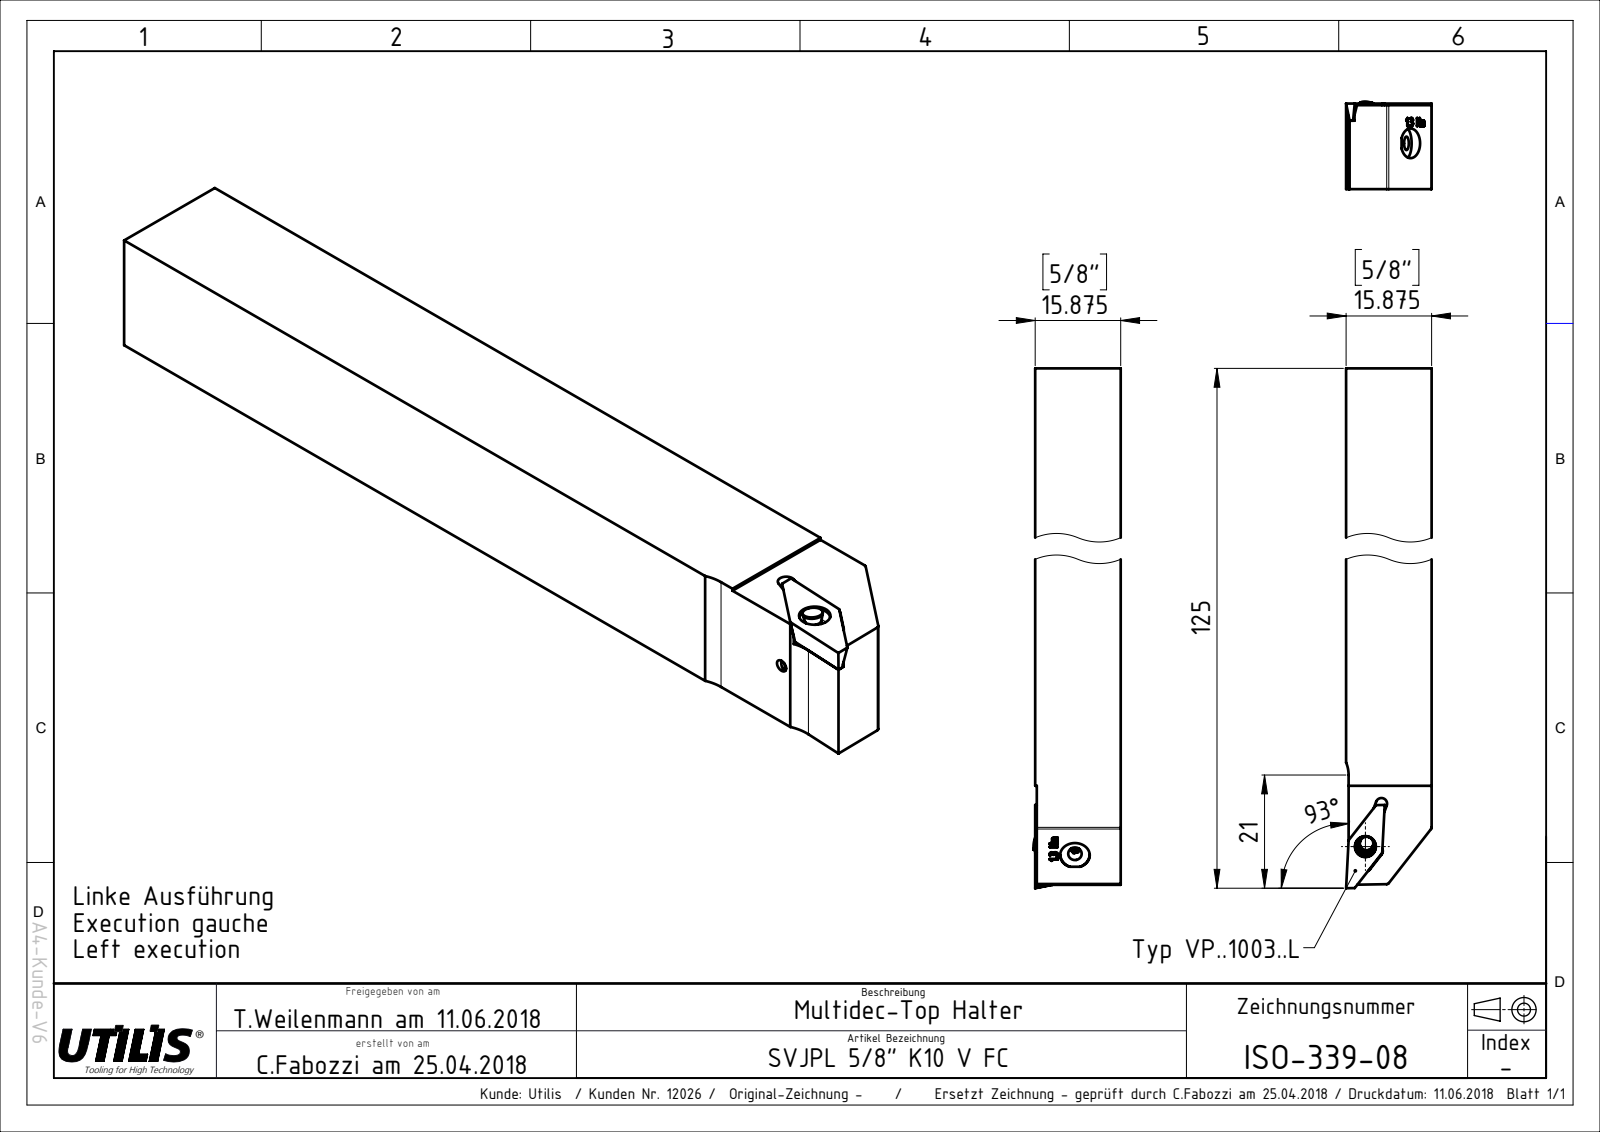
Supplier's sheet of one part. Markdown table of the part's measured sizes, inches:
| quantity | value |
| --- | --- |
| part name | ISO-339-08 |
| STEP written by | SolidWorks 2018 (AUTOMOTIVE_DESIGN) |
| units | inches |
| bodies | 1 solid, 116 faces (58 planar, 9 cylindrical, 49 other) |
| overall size | 4.921 × 0.637 × 0.625 |
| volume | 1.854 in³ |
| surface area | 12.89 in² |
| partial cylindrical surfaces (radius × count) | 0.041 × 3, 0.02 × 2, 0.049 × 1, 0.236 × 1, 0.24 × 1 |
| main face-to-face distances | 0.625, 0.019, 0.607, 0.613, 0.5, 0.113, 0.125, 0.17, 0.408, 0.238 |
